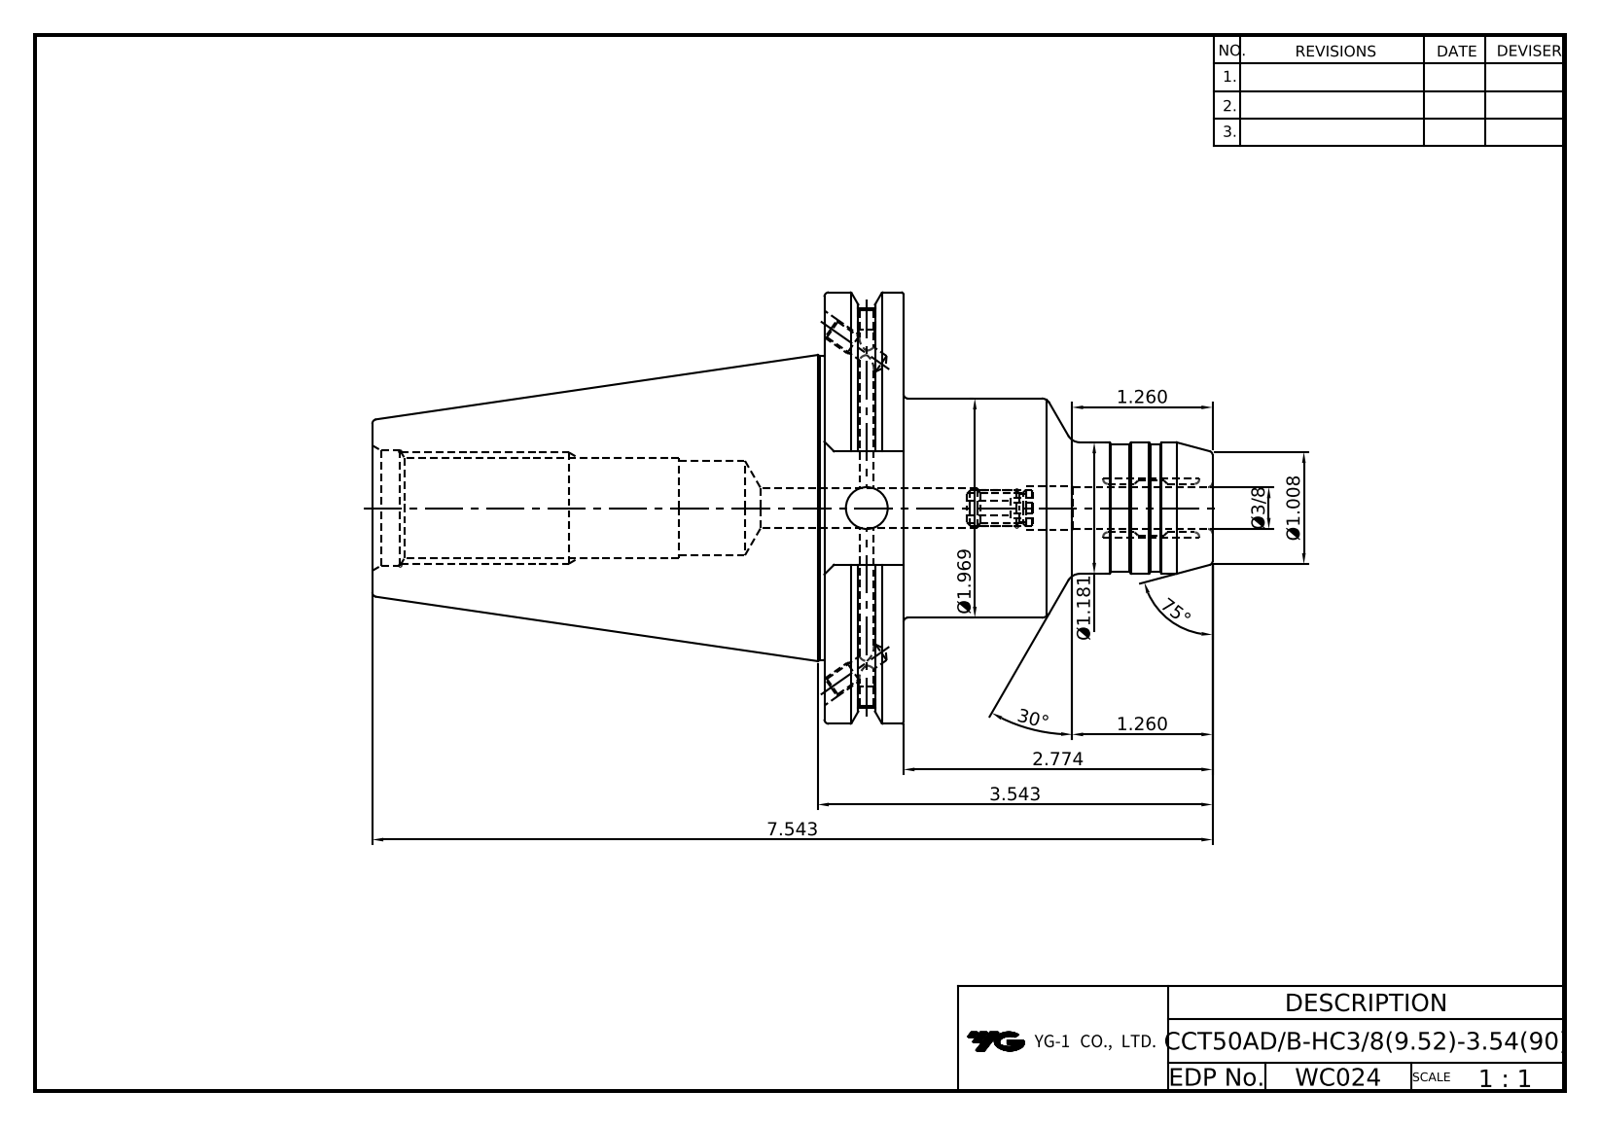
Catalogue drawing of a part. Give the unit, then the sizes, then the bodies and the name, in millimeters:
Units: millimetres
Overall size (bounding box): 191.6 × 98.42 × 94.69
Round holes (diameter × count): ⌀3.24 ×2, ⌀4.13 ×2, ⌀4.2 ×2, ⌀5 ×2, ⌀9.53 ×2, ⌀6.92 ×1, ⌀9 ×1, ⌀10 ×1, ⌀21.5 ×1, ⌀21.97 ×1, ⌀26.2 ×1
Round bosses / shafts (diameter × count): ⌀98.42 ×1, ⌀91.29 ×1, ⌀69.25 ×1, ⌀50 ×1, ⌀30 ×1, ⌀29 ×1
Main face-to-face distances: 17.55, 103.1, 120.65, 191.6, 88.5, 70.95, 73.03, 25.9, 103.5, 0.4
Volume: 423 448 mm³ · Surface area: 54 409 mm²
Bodies: 1 solid, 110 faces (38 planar, 33 cylindrical, 39 other)
Part name (STEP PRODUCT): CCT50ADB-HC9.525-90
STEP written by: Autodesk Inventor 2022 (AUTOMOTIVE_DESIGN)
